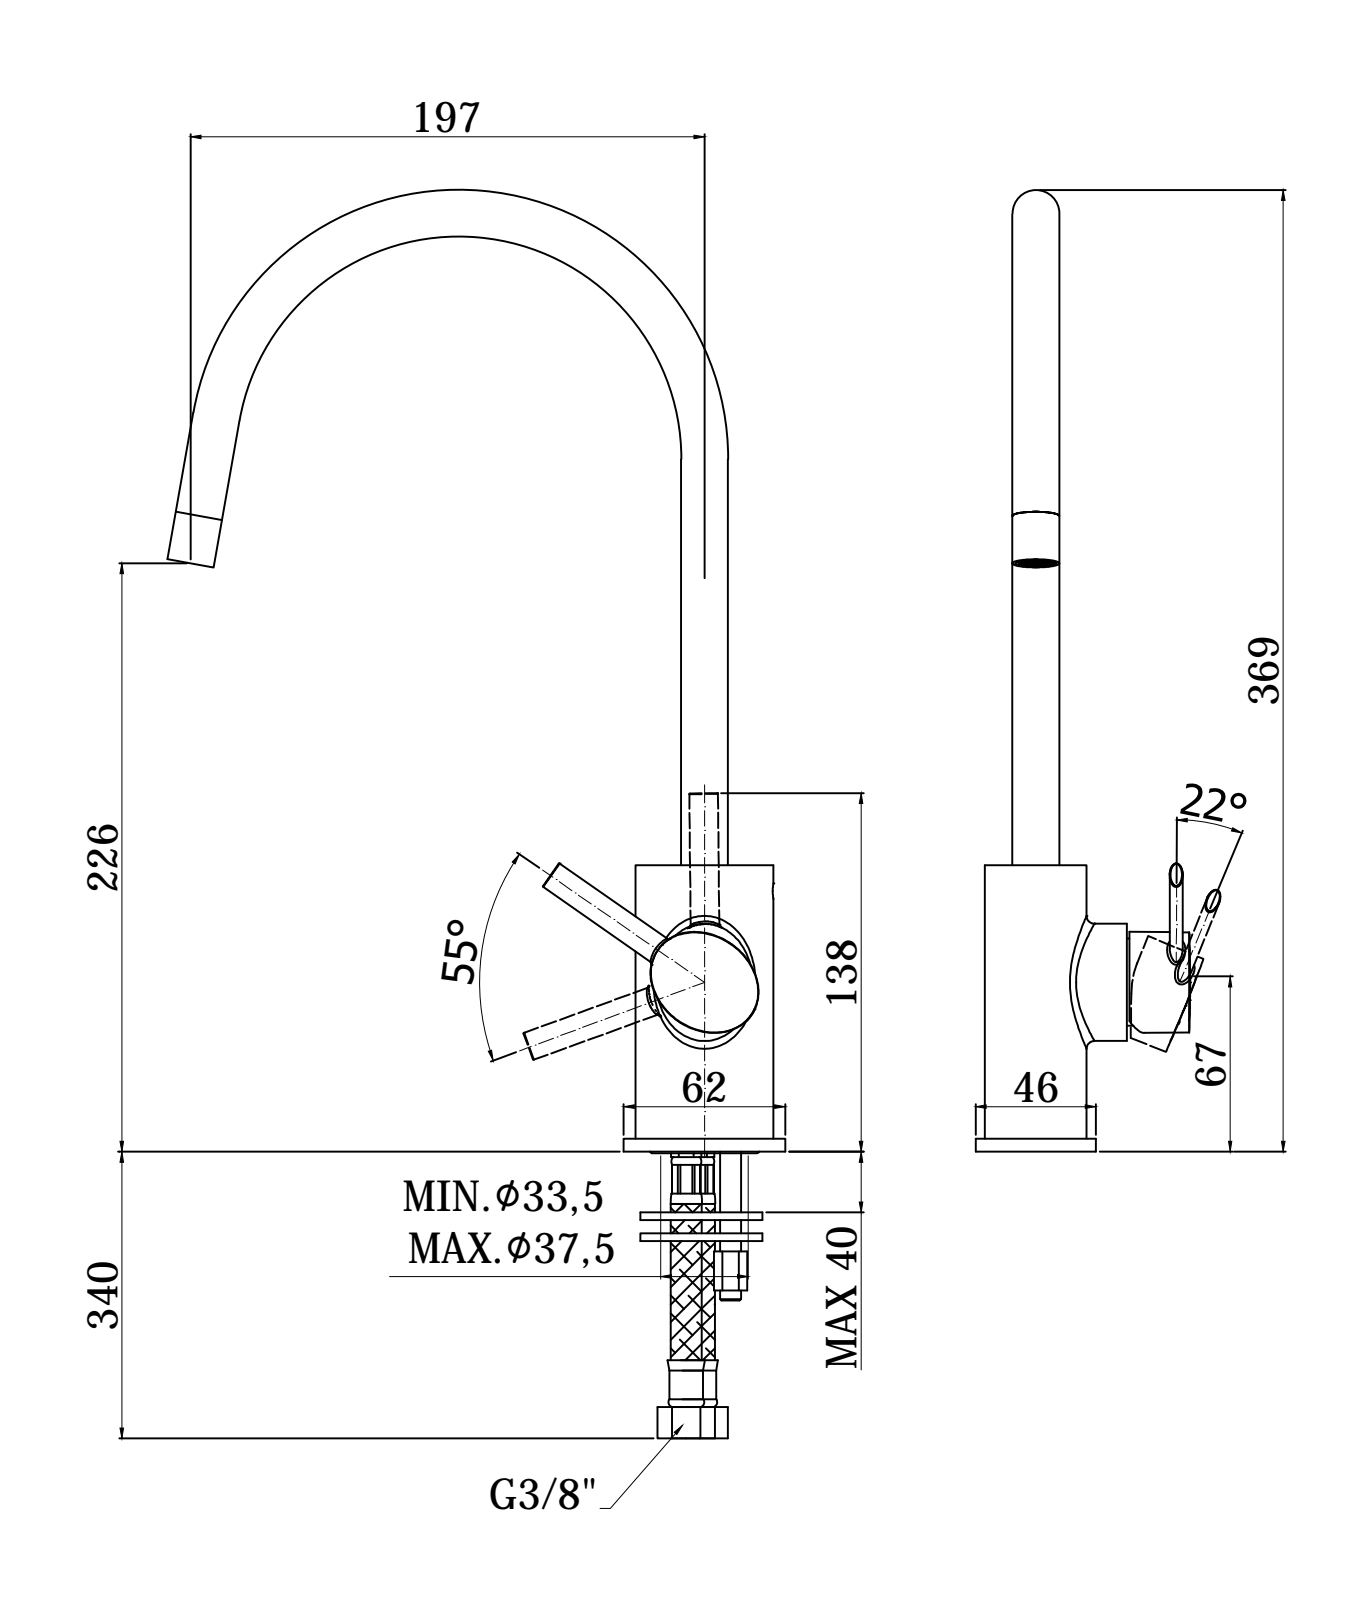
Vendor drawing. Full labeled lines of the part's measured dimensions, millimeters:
Part name (STEP PRODUCT): BR180CR
STEP written by: CREO PARAMETRIC BY PTC INC, 2020044 (CONFIG_CONTROL_DESIGN)
Units: millimetres
Bodies: 2 solids, 1384 faces (577 planar, 523 cylindrical, 284 other)
Overall size (bounding box): 369.42 × 236.29 × 83.2
Volume: 231 063 mm³ · Surface area: 105 621 mm²
Round holes (diameter × count): ⌀0.5 ×51, ⌀5 ×4, ⌀6 ×4, ⌀15 ×3, ⌀3 ×2, ⌀5.5 ×2, ⌀8.6 ×2, ⌀9.4 ×2, ⌀4.5 ×1, ⌀7.5 ×1, ⌀11 ×1, ⌀12 ×1
Round bosses / shafts (diameter × count): ⌀18 ×2, ⌀38.8 ×1, ⌀28.5 ×1, ⌀27.8 ×1, ⌀25 ×1, ⌀20 ×1, ⌀19 ×1, ⌀15.7 ×1
Partial cylindrical surfaces — rounded edges, fillets, slot ends (radius × count): R0.5 ×40, R0.3 ×17, R1 ×17, R0.2 ×13, R0.15 ×10, R2 ×10, R1.25 ×4, R2.45 ×4
Main face-to-face distances: 110, 3, 5, 2, 8, 102, 1.9, 105, 9, 3.2
Hole centre spacings: 3.35, 1.5, 2.12, 4.74, 3, 5.41, 4.24, 4.5
